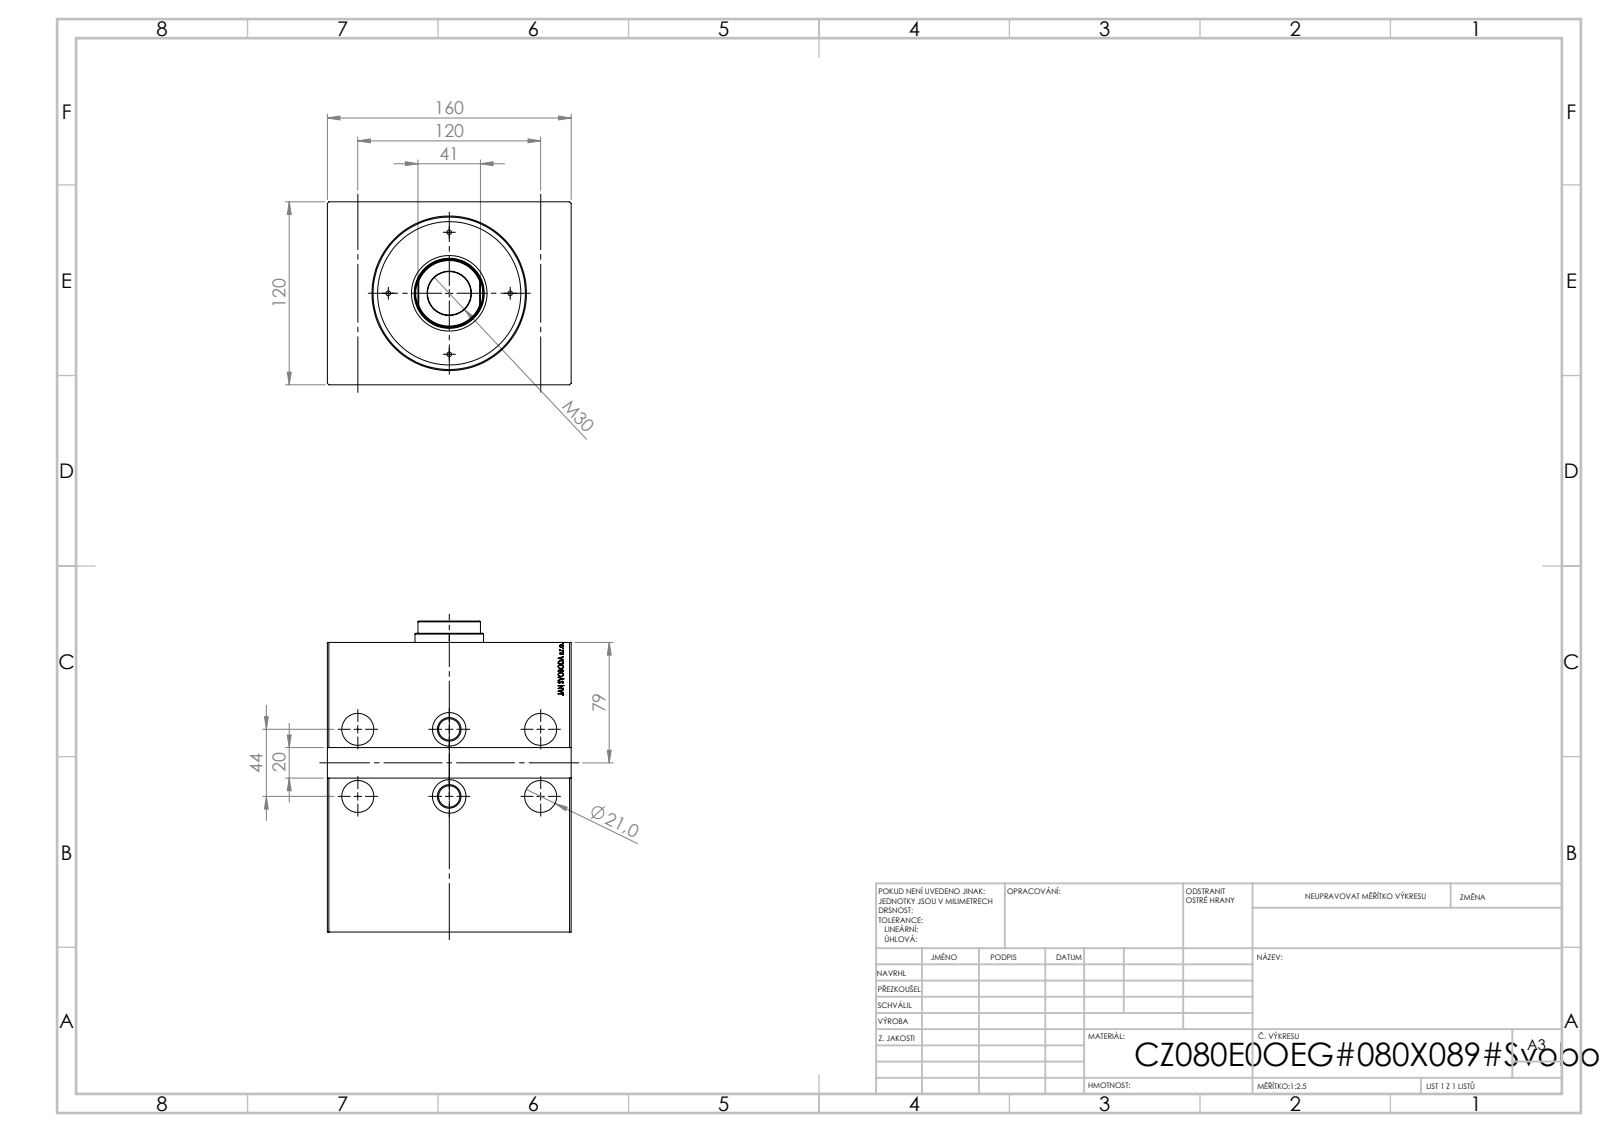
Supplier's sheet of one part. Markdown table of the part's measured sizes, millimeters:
| quantity | value |
| --- | --- |
| STEP written by | SolidWorks 2019 (CONFIG_CONTROL_DESIGN) |
| units | millimeters |
| bodies | 1 solid, 807 faces (395 planar, 30 cylindrical, 382 other) |
| overall size | 190 × 160 × 120 |
| volume | 2 605 000 mm³ |
| surface area | 216 927 mm² |
| round holes (diameter × count) | 21 × 4, 8 × 2, 14 × 2, 22 × 2, 36 × 1, 80 × 1, 100 × 1 |
| round bosses / shafts (diameter × count) | 15.5 × 2 |
| main face-to-face distances | 120, 160, 190, 164.7, 25.3, 2, 118, 14, 150.7, 176 |
| hole center spacings | 60, 74.4, 44, 120, 127.81, 28.23, 35.74, 60.84 |
